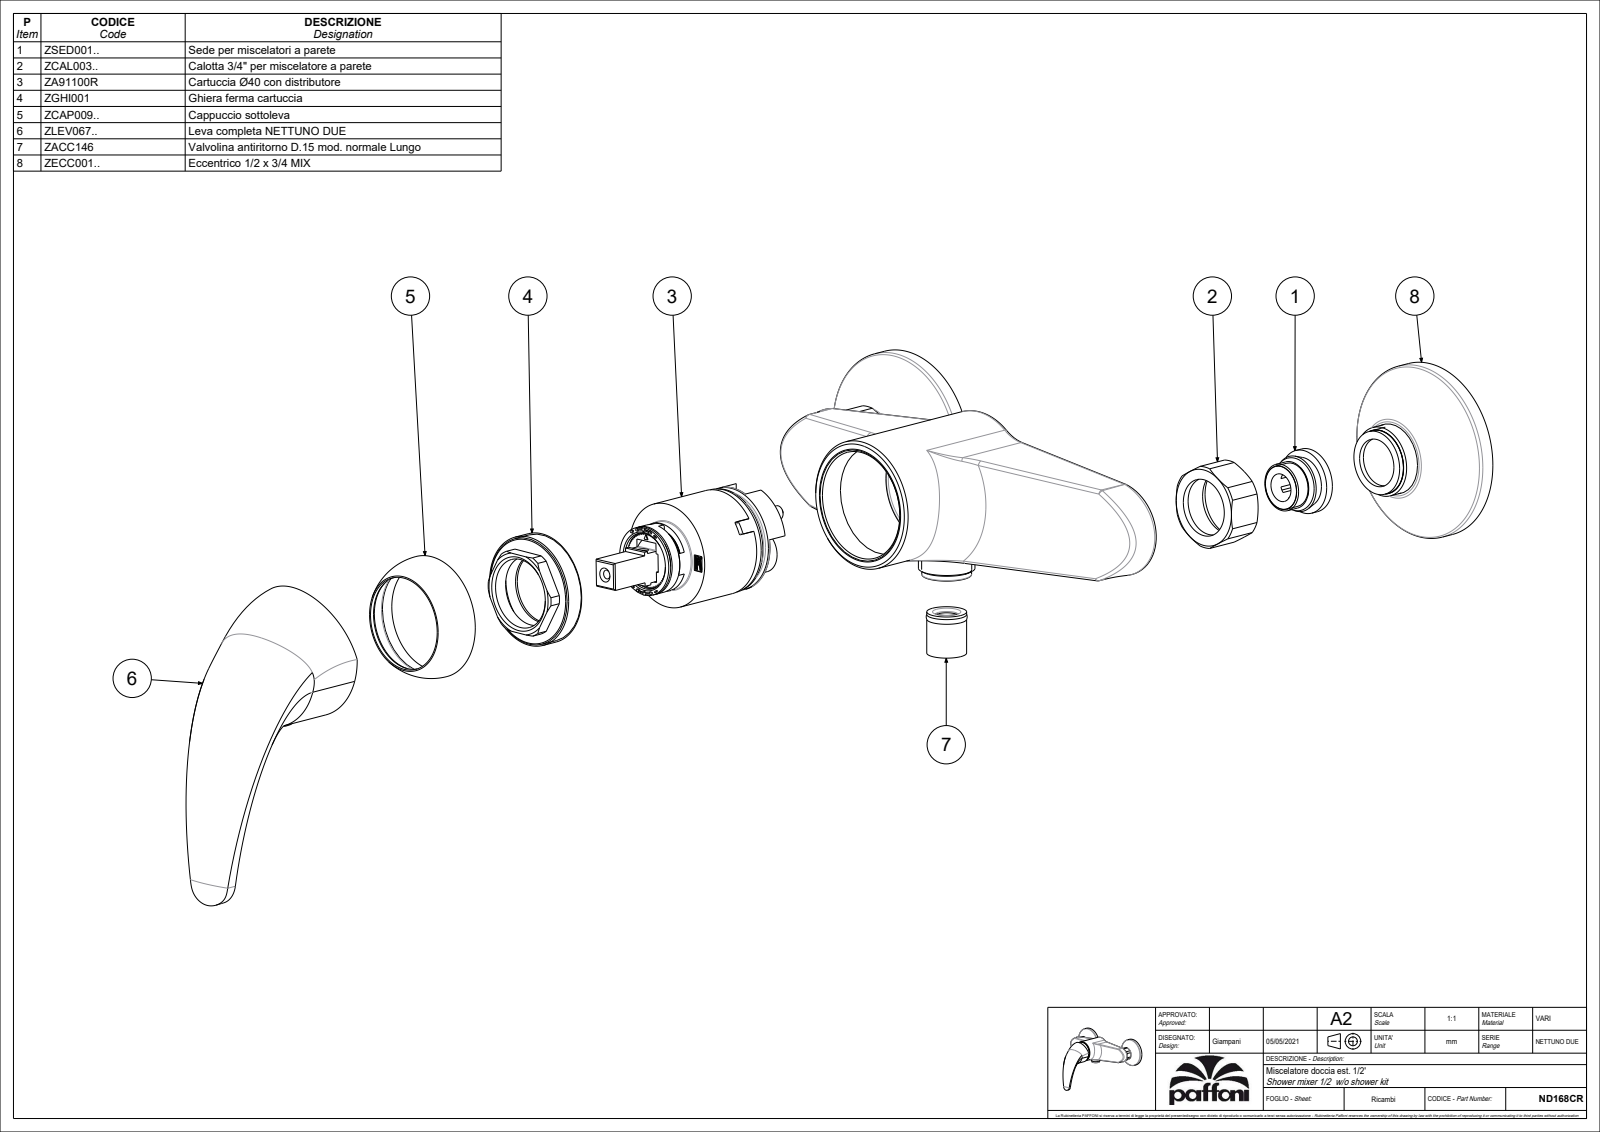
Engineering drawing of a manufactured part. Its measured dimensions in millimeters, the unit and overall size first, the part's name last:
Units: millimetres
Overall size (bounding box): 215.5 × 159 × 114.13
Round holes (diameter × count): ⌀6 ×1
Round bosses / shafts (diameter × count): ⌀65.5 ×2, ⌀48.5 ×1, ⌀21 ×1, ⌀18.5 ×1, ⌀5 ×1
Partial cylindrical surfaces — rounded edges, fillets, slot ends (radius × count): R15.5 ×2, R2 ×1, R3.9 ×1, R4 ×1
Main face-to-face distances: 35.5, 29, 114, 78.5, 34, 1.5, 80, 75, 0.5, 104
Volume: 426 887 mm³ · Surface area: 64 140 mm²
Bodies: 1 solid, 202 faces (51 planar, 33 cylindrical, 118 other)
Part name (STEP PRODUCT): ND168CR
STEP written by: CREO PARAMETRIC BY PTC INC, 2020044 (CONFIG_CONTROL_DESIGN)
